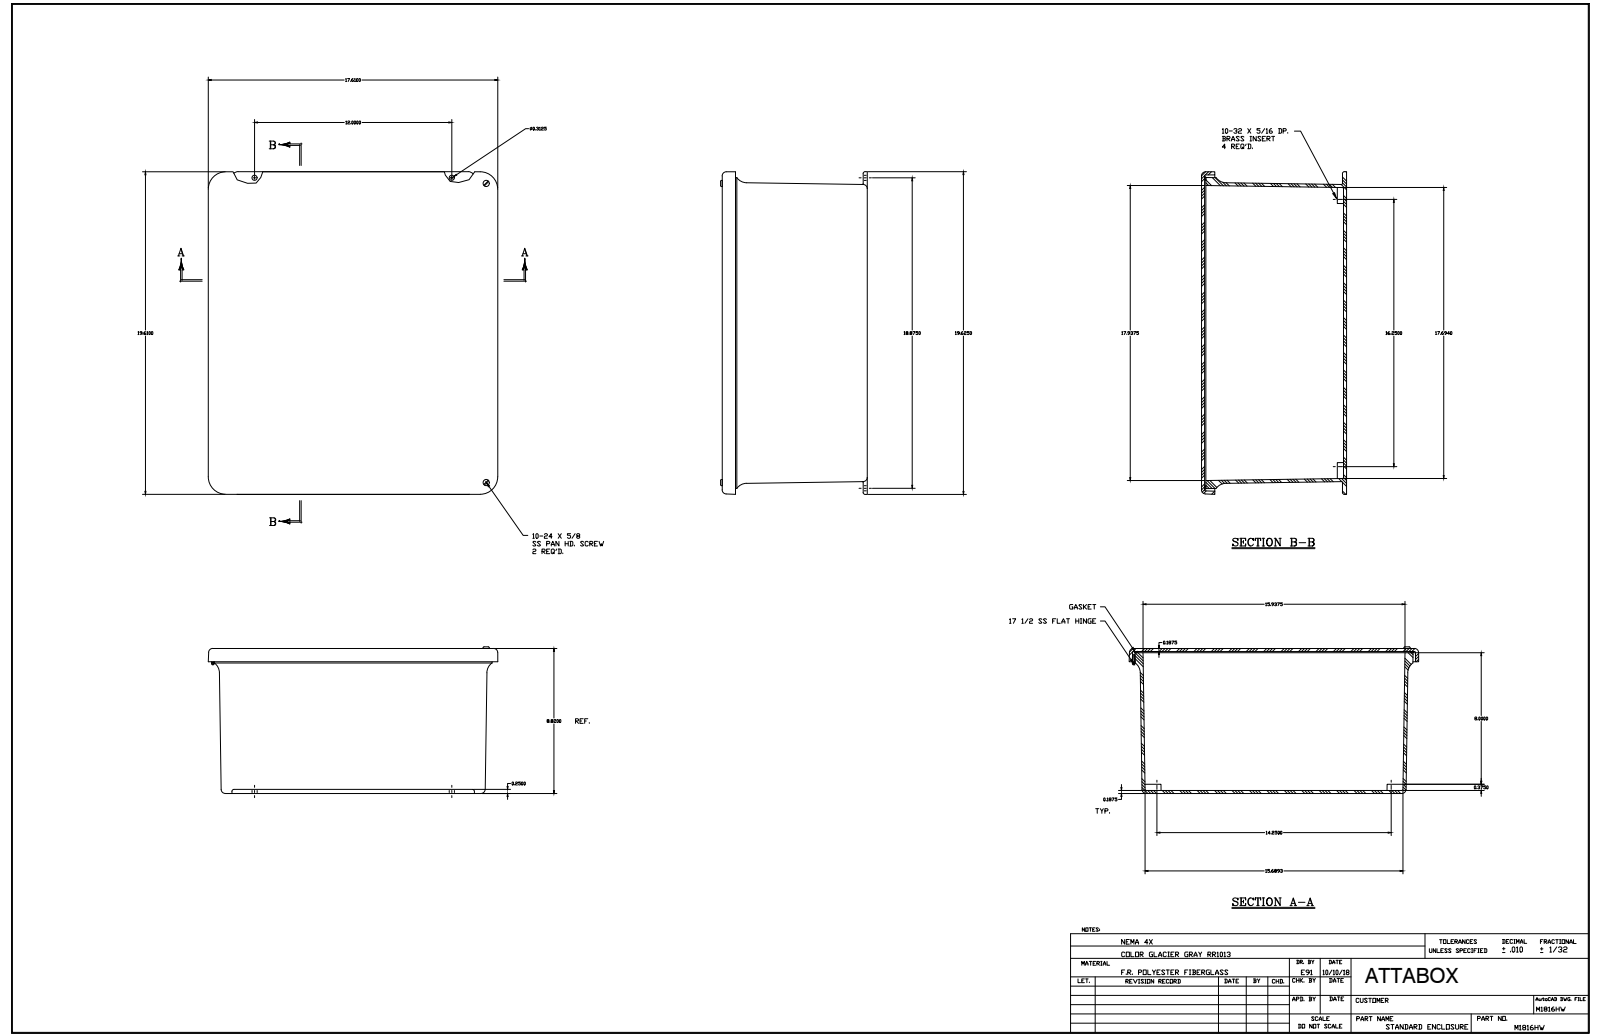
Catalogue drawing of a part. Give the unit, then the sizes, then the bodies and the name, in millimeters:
Units: millimetres
Overall size (bounding box): 498.5 × 448.1 × 227.5
Round holes (diameter × count): ⌀3.3 ×12, ⌀3.6 ×12, ⌀3.9 ×5, ⌀4 ×4, ⌀5.5 ×4, ⌀3.7 ×2, ⌀2.2 ×1
Round bosses / shafts (diameter × count): ⌀6.4 ×12, ⌀3.2 ×9, ⌀6.9 ×6, ⌀3.2 ×3, ⌀4.8 ×2, ⌀4 ×2, ⌀3.9 ×1, ⌀3.9 ×1
Partial cylindrical surfaces — rounded edges, fillets, slot ends (radius × count): R0.8 ×20, R3.2 ×12, R6.4 ×8, R5.1 ×6, R9.5 ×4, R19.1 ×4, R1.6 ×2
Main face-to-face distances: 4.7, 219.4, 224.2, 4.8, 214.6, 219.4, 12.4, 7.7, 217.5, 212.7
Hole centre spacings: 85.7, 85.7, 171.5, 260.4, 6.4, 247.7, 254, 34.8
Volume: 4 254 000 mm³ · Surface area: 1 741 000 mm²
Bodies: 26 solids, 953 faces (369 planar, 371 cylindrical, 213 other)
Part name (STEP PRODUCT): M1816HW
STEP written by: SolidWorks 2018 (AUTOMOTIVE_DESIGN)
